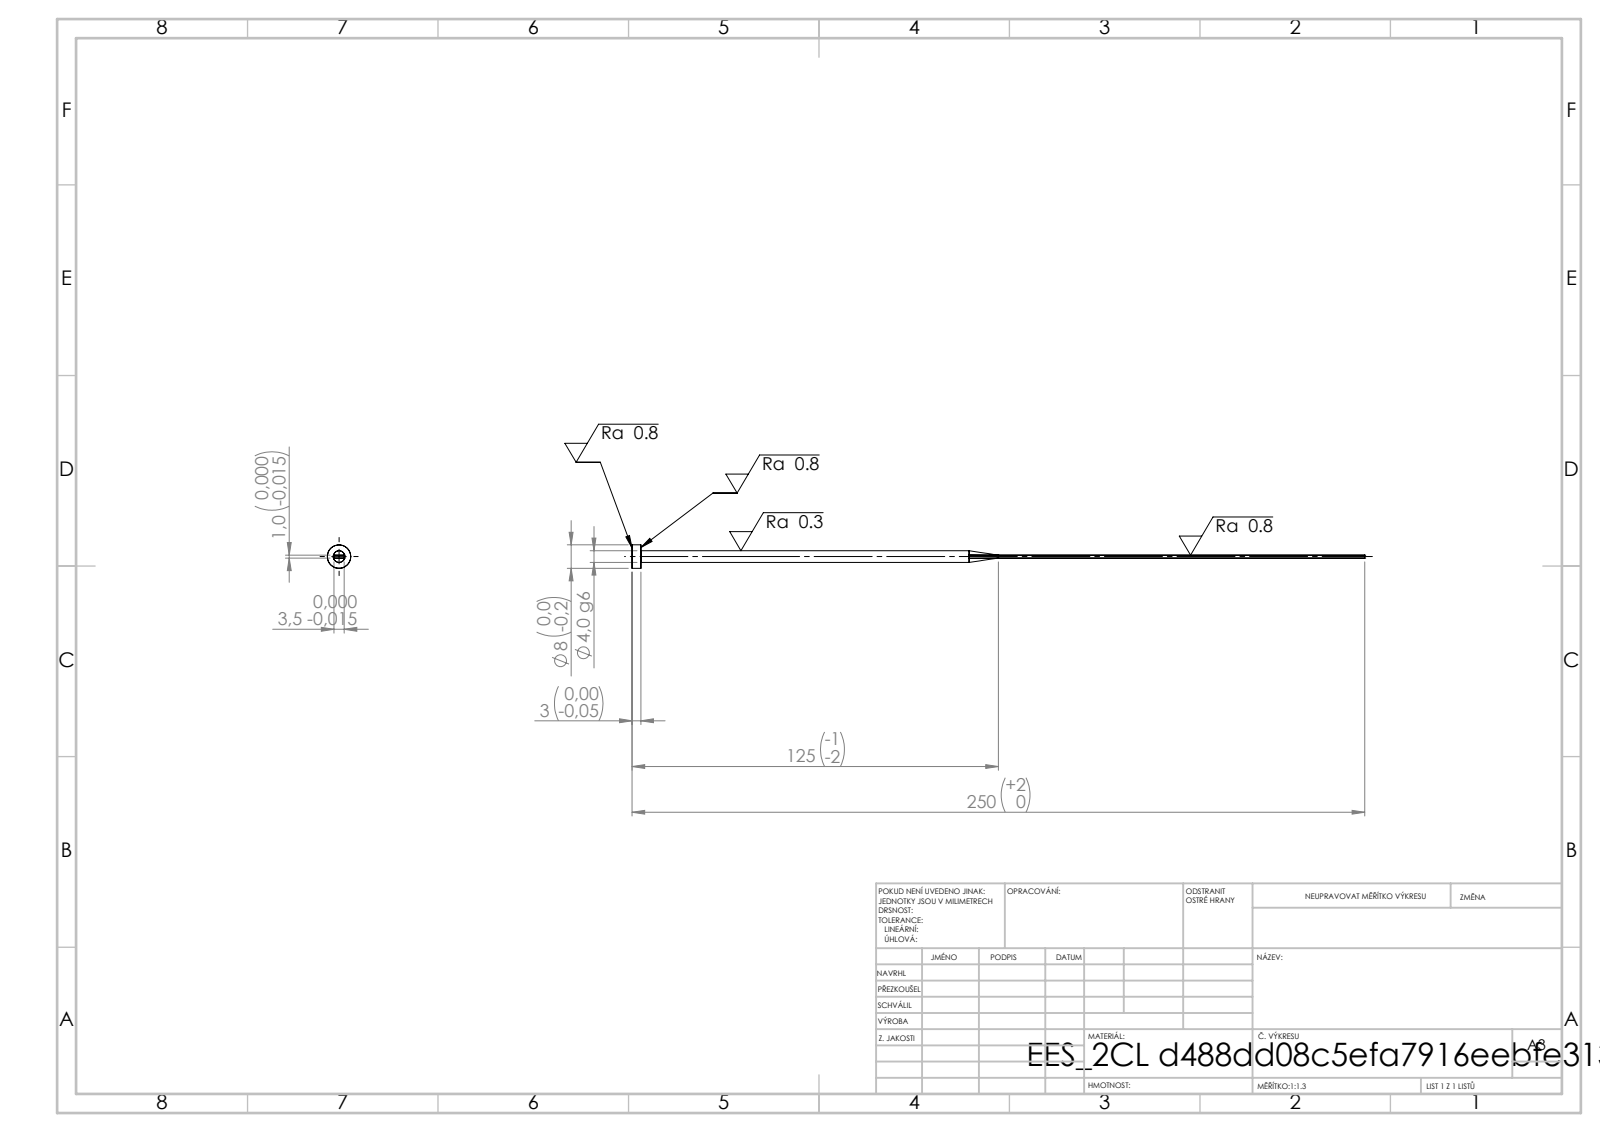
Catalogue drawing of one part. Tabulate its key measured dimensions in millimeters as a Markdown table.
| quantity | value |
| --- | --- |
| STEP written by | SolidWorks 2019 (CONFIG_CONTROL_DESIGN) |
| units | millimeters |
| bodies | 1 solid, 15 faces (7 planar, 4 cylindrical, 4 other) |
| overall size | 250 × 8 × 8 |
| volume | 2 073 mm³ |
| surface area | 2 804 mm² |
| round bosses / shafts (diameter × count) | 8 × 1, 4 × 1 |
| main face-to-face distances | 1, 3.5, 3, 250, 247 |
